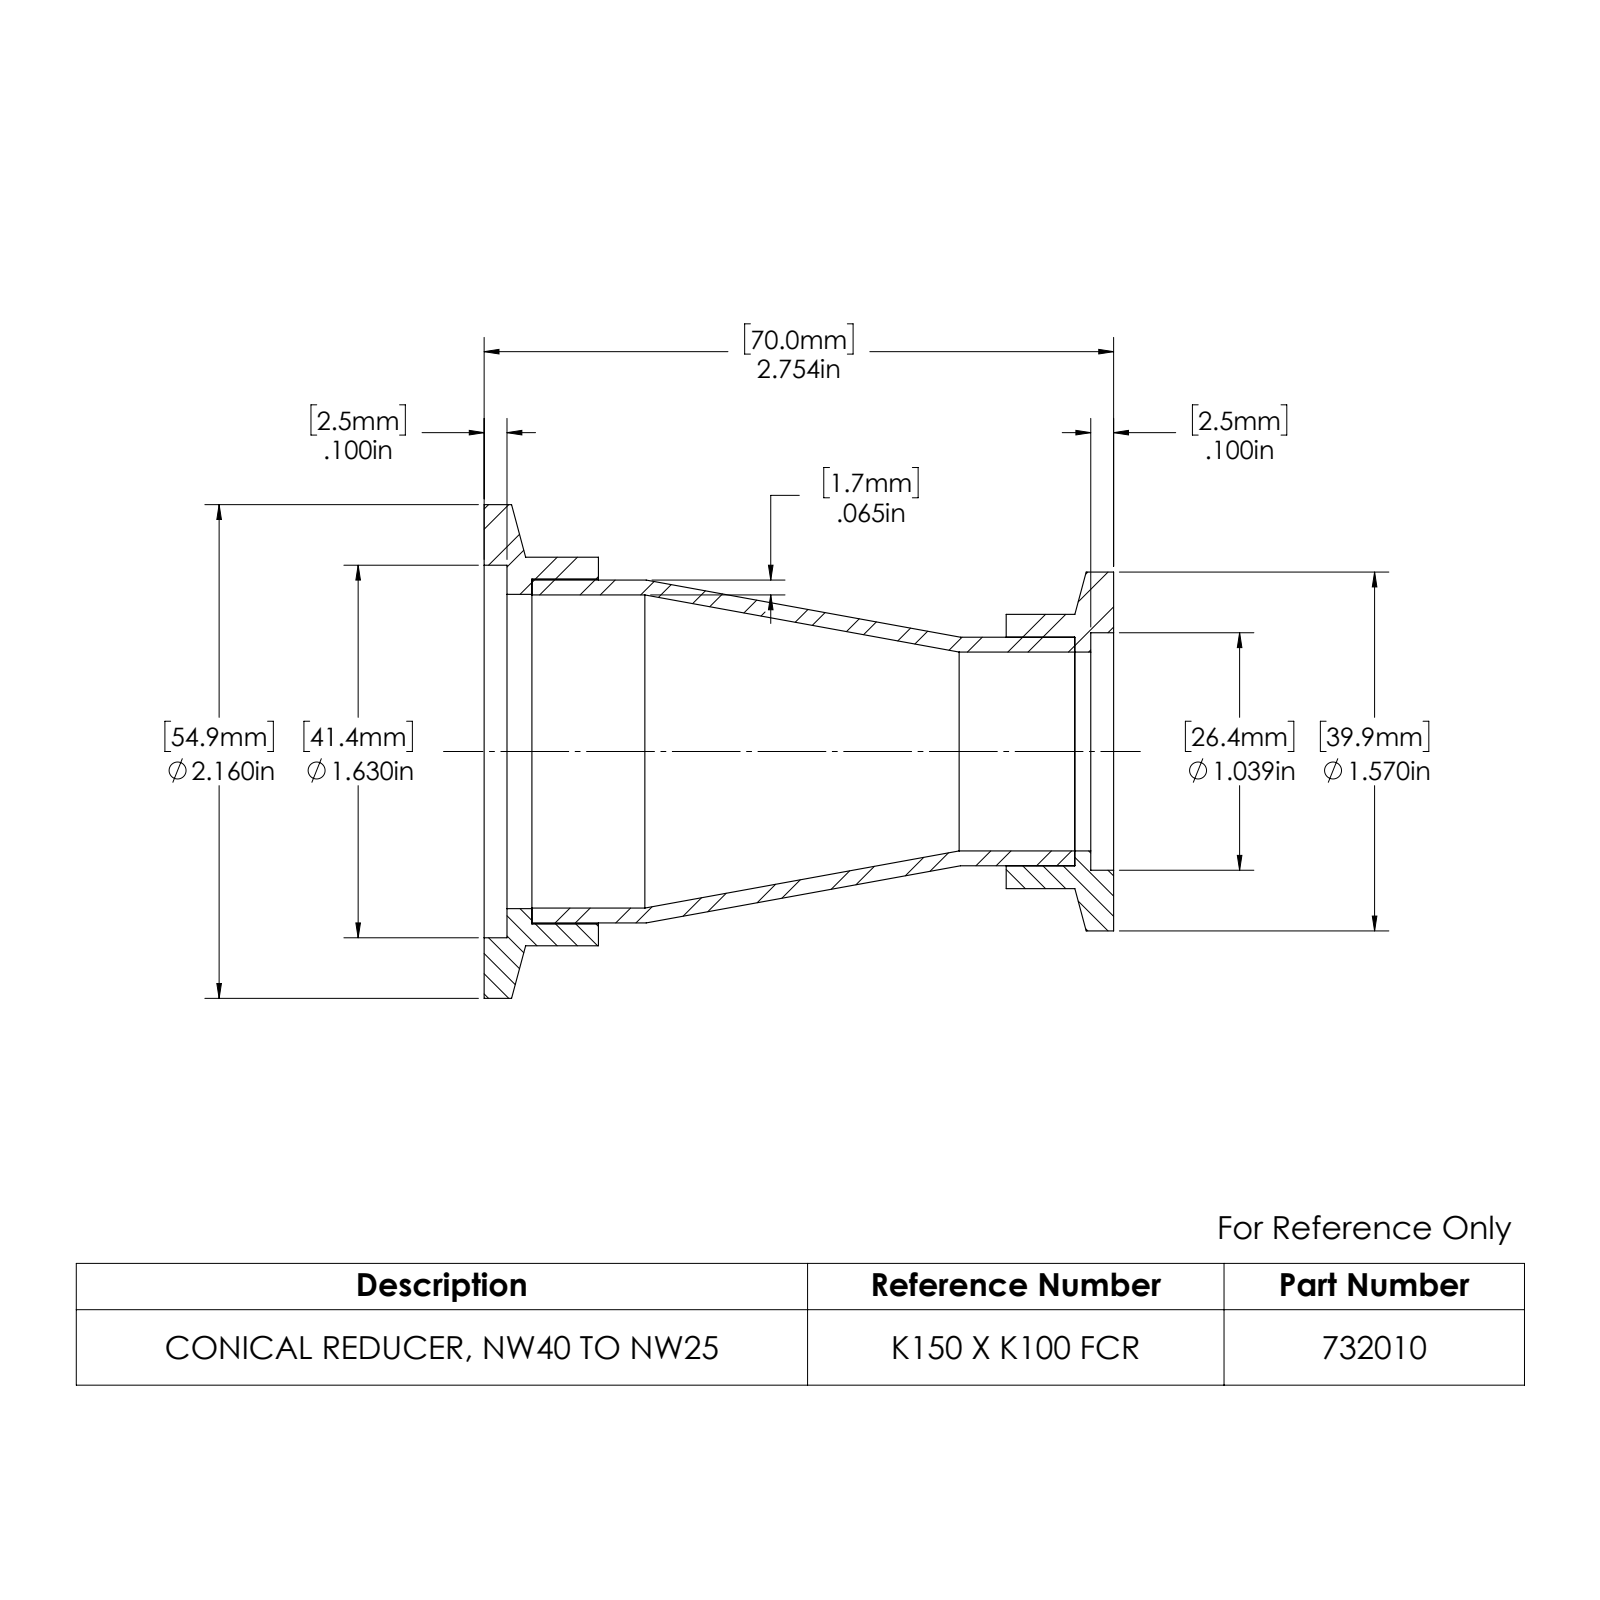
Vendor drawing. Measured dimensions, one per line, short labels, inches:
name: 732010
written by: SolidWorks 2022 (AUTOMOTIVE_DESIGN)
unit: in
bodies: 3 solids, 46 faces (10 planar, 28 cylindrical, 8 other)
size: 2.754 × 2.16 × 2.16
volume: 1.317 in³; area: 33.51 in²
holes: 1× ⌀0.87, 1× ⌀1, 1× ⌀1.039, 1× ⌀1.37, 1× ⌀1.375, 1× ⌀1.51, 1× ⌀1.63
bosses: 1× ⌀2.16, 1× ⌀1.7, 1× ⌀1.57, 1× ⌀1.5, 1× ⌀1.2
face distances: 2.754, 0.1, 2.654, 0.209, 0.109, 2.545, 0.5, 0.4, 0.291, 2.254
